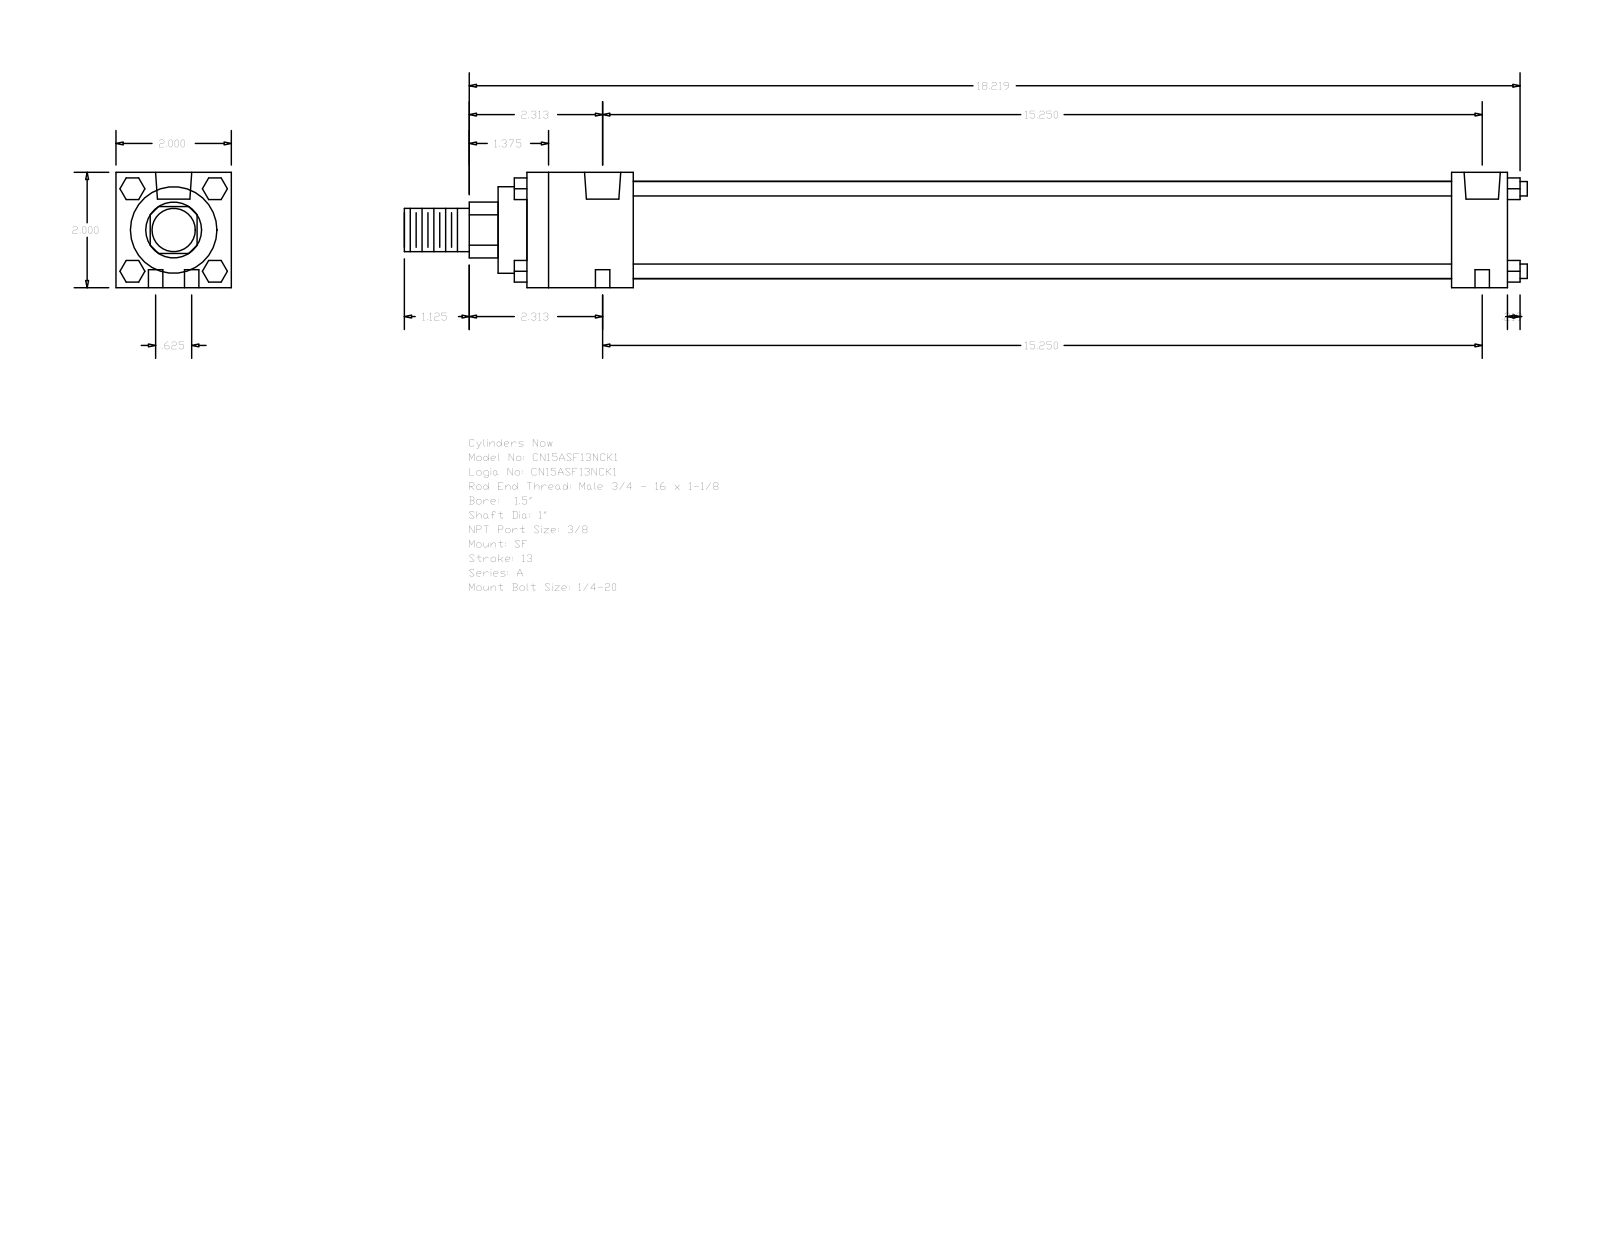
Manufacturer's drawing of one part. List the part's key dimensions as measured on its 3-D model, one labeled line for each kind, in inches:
Part name (STEP PRODUCT): A_SF__0150_1
STEP written by: GSSL Pune (CONFIG_CONTROL_DESIGN)
Units: inches
Bodies: 0 solids, 124 faces (94 planar, 30 cylindrical, 0 other)
Overall size (bounding box): 19.469 × 2 × 2
Round holes (diameter × count): ⌀0.25 ×4, ⌀0.219 ×2, ⌀0.627 ×2
Round bosses / shafts (diameter × count): ⌀0.25 ×4, ⌀1.69 ×1, ⌀1.5 ×1, ⌀1 ×1, ⌀0.75 ×1
Partial cylindrical surfaces — rounded edges, fillets, slot ends (radius × count): R0.484 ×1
Main face-to-face distances: 2, 17, 1.844, 16.031, 14.187, 15.156, 0.969, 0.5, 2.344, 16.531
Hole centre spacings: 0.313, 15.253, 15.25, 0.625, 15.263, 14.937
